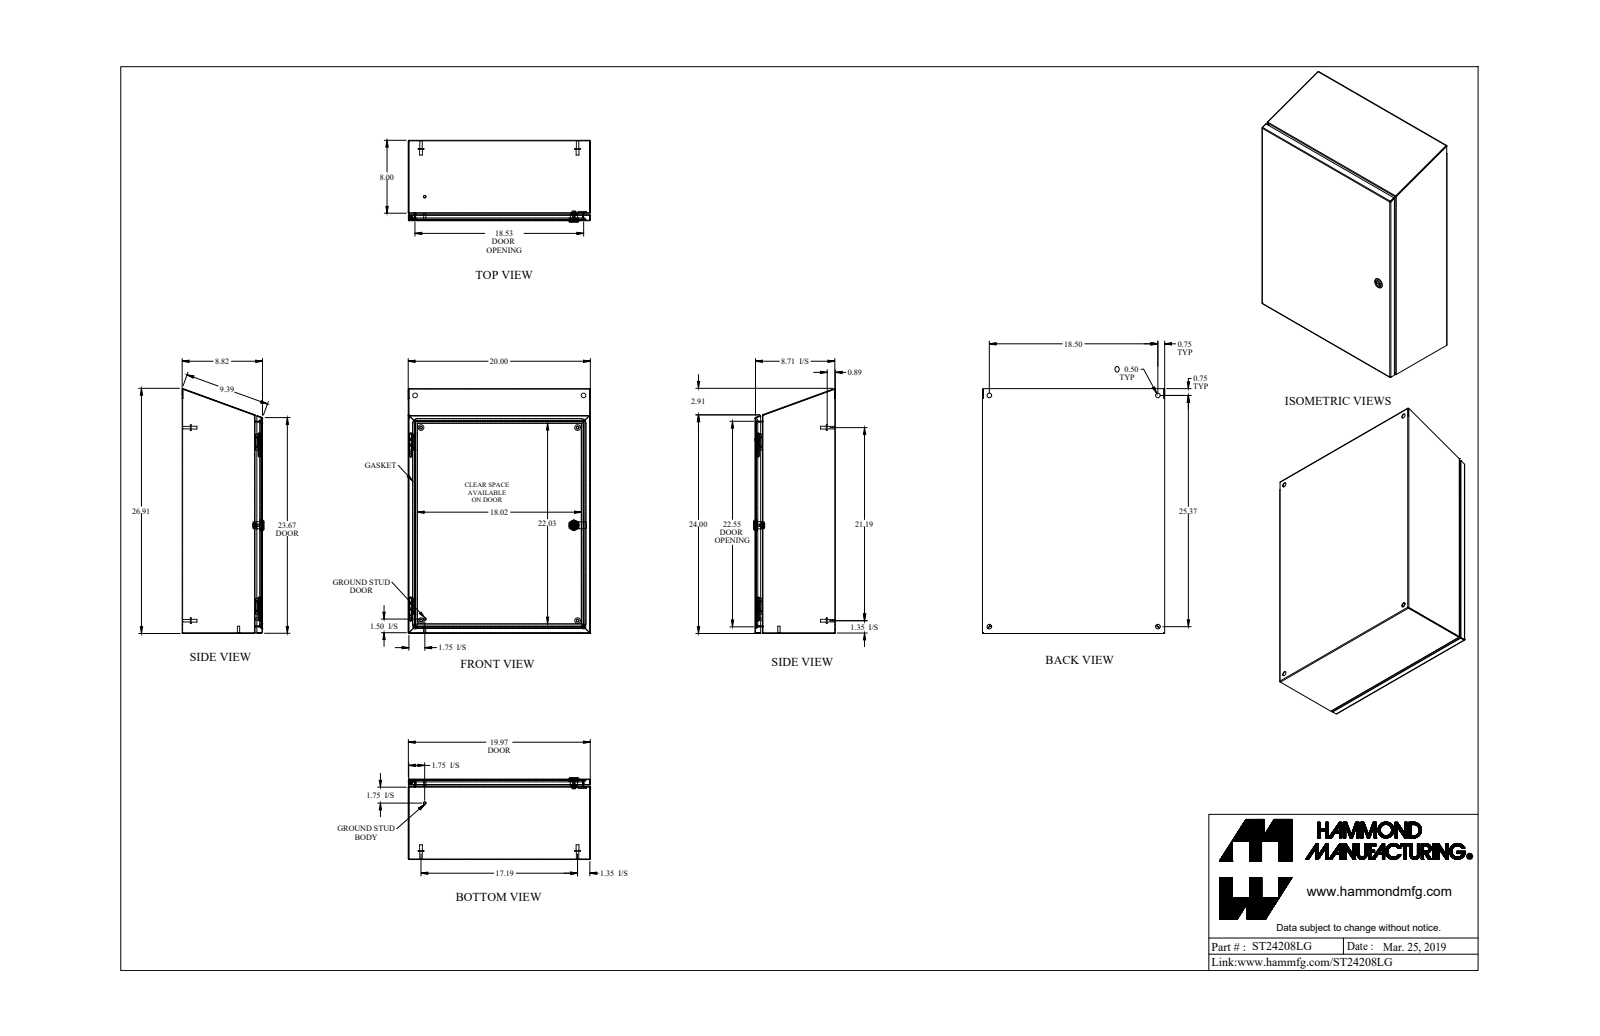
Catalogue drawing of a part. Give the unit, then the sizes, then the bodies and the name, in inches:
Units: inches
Overall size (bounding box): 26.875 × 20 × 8.982
Round holes (diameter × count): ⌀0.5 ×4, ⌀0.172 ×1, ⌀0.232 ×1, ⌀0.24 ×1, ⌀0.242 ×1, ⌀0.625 ×1, ⌀0.785 ×1
Round bosses / shafts (diameter × count): ⌀0.625 ×4, ⌀0.313 ×4, ⌀0.27 ×4, ⌀0.281 ×2, ⌀0.25 ×2, ⌀1.1 ×1, ⌀0.525 ×1, ⌀0.455 ×1
Partial cylindrical surfaces — rounded edges, fillets, slot ends (radius × count): R0.029 ×21, R0.086 ×21, R0.25 ×11, R0.006 ×4, R0.062 ×4, R0.499 ×4, R0.125 ×2, R0.021 ×1
Main face-to-face distances: 0.057, 0.057, 8.765, 8.708, 8.822, 8.765, 19.943, 19.886, 20, 0.822
Hole centre spacings: 18.5, 25.374, 31.402, 11.178, 14.286, 20.688, 22.52
Volume: 118 in³ · Surface area: 4 034 in²
Bodies: 21 solids, 632 faces (303 planar, 197 cylindrical, 132 other)
Part name (STEP PRODUCT): ST24208LG
STEP written by: SolidWorks 2018 (AUTOMOTIVE_DESIGN)
